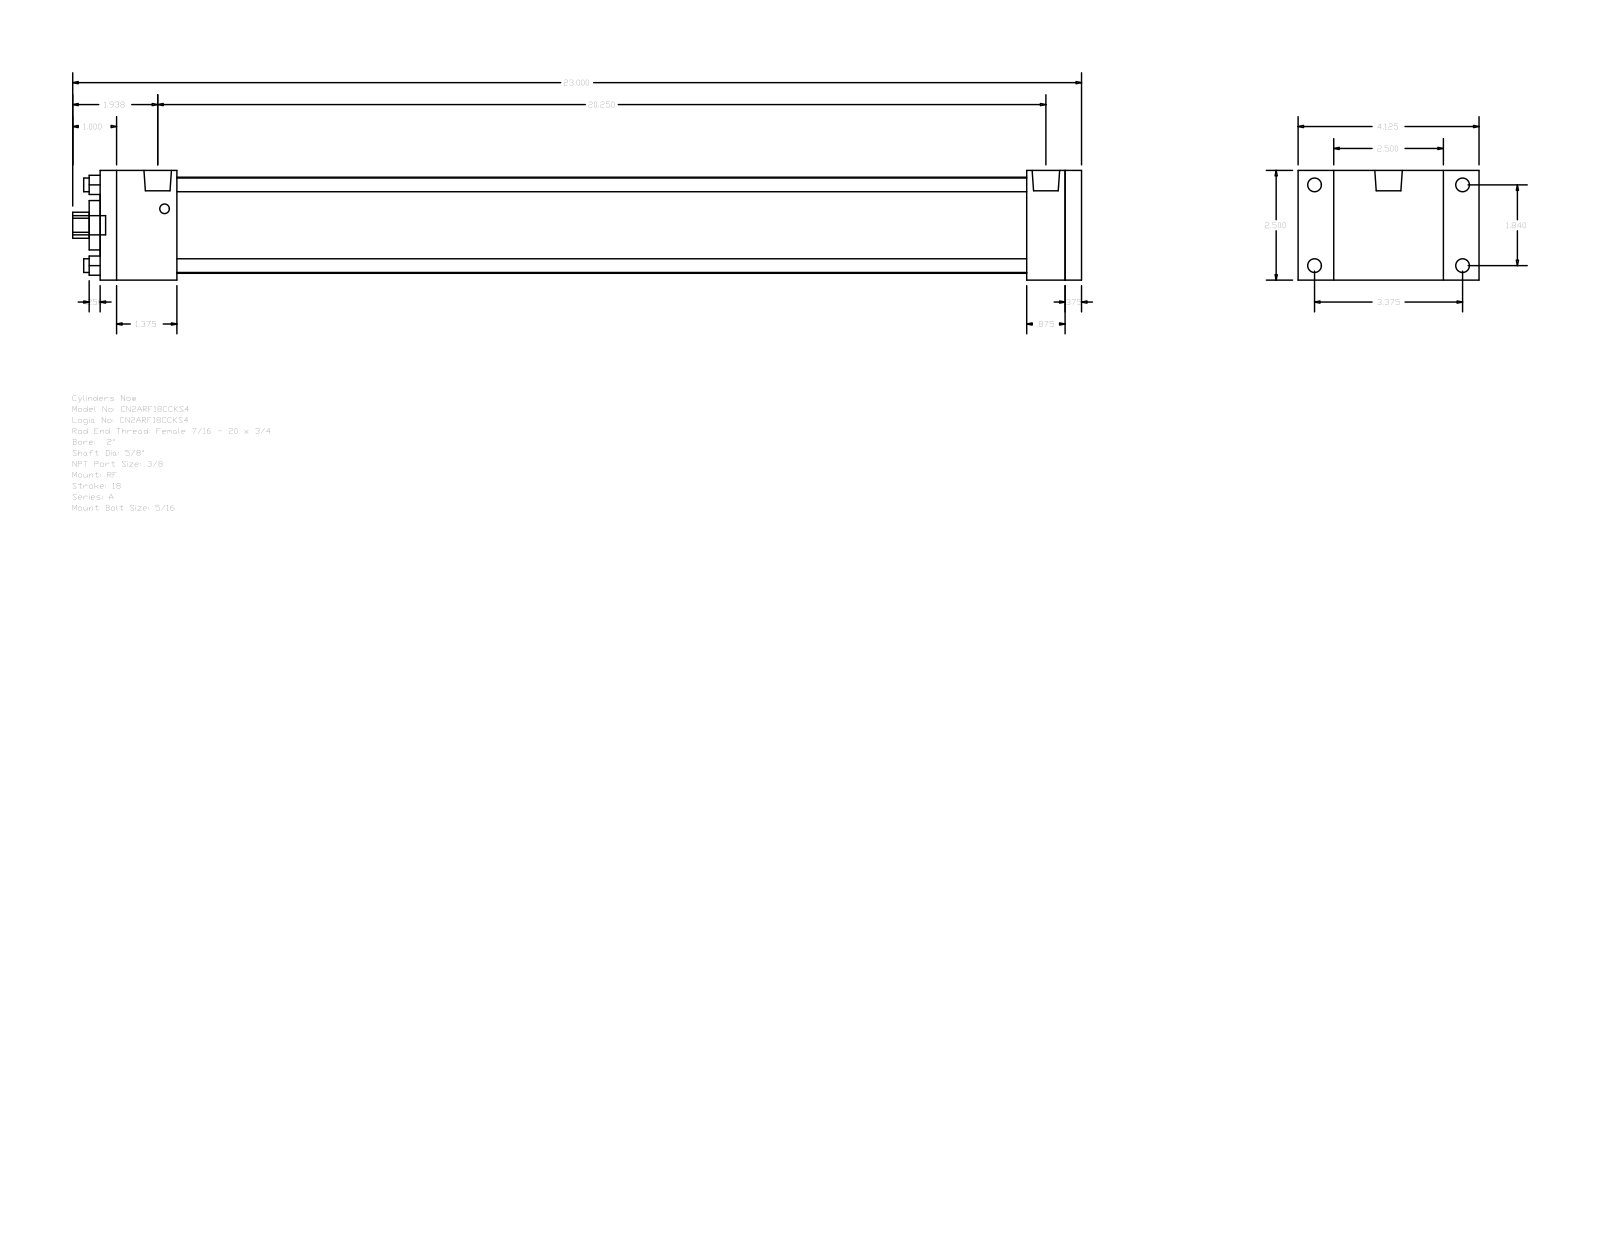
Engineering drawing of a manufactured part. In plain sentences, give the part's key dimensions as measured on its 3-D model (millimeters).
The part is named "A_RF__0200_0.625". Its 3-D file was written by "GSSL Pune (CONFIG_CONTROL_DESIGN)". It is 0 solids with 92 faces: 64 planar, 28 cylindrical and 0 other. Overall it measures 584.2 by 104.78 by 63.5 millimeters. Round holes: 4 of diameter 7.94, 1 of diameter 15.88, 1 of diameter 28.57, 1 of diameter 55.63. Round bosses or shafts: 4 of diameter 7.94, 4 of diameter 5.56, 2 of diameter 15.93, 1 of diameter 11.11. Partial cylindrical surfaces (rounded edges, fillets, slot ends): 1 of radius 7.54. The main face-to-face distances are 63.5, 568.32, 9.53, 558.79, 44.45, 514.34, 523.87, 536.57, 492.12, 22.22. The hole center spacings are 33.05, 46.74, 66.1.
